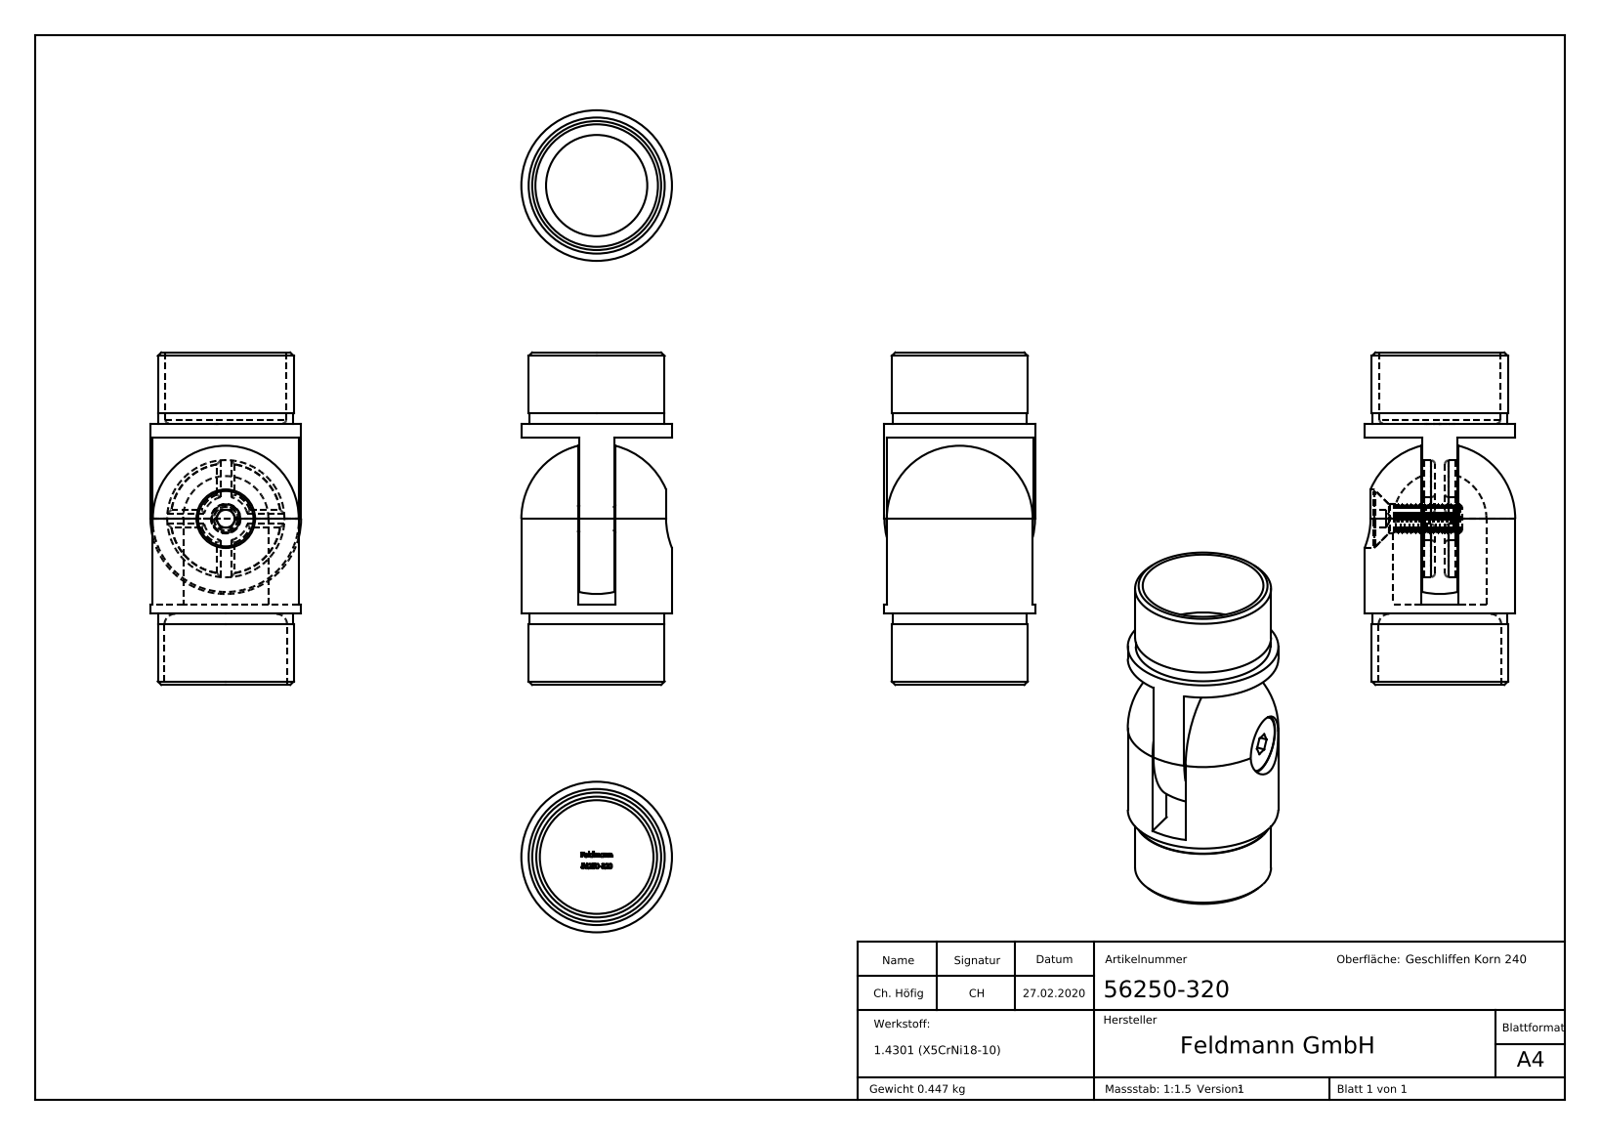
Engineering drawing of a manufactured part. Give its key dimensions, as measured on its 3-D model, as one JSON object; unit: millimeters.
{"part_name": "socket countersunk head screw_din_DIN 7991 - M8 x 25 --- 25S; 5625X-320 Teil2; 5625X-320 Teil1_56250-320 Teil1; 5625X-320 Teil2_56250-320 Teil2 (+3 more)", "step_written_by": "SolidWorks 2015 (CONFIG_CONTROL_DESIGN)", "units": "millimeters", "bodies": {"solids": 3, "faces": 403, "planar": 168, "cylindrical": 56, "other": 179}, "overall_size": [93.6, 42.4, 42.4], "volume_mm3": 57804, "surface_area_mm2": 29843, "round_holes": [[6.8, 1], [8.2, 1], [16.5, 1], [33, 1], [34, 1], [34.5, 1]], "round_bosses_or_shafts": [[42.4, 1], [38.3, 1], [37.9, 1], [15.57, 1], [8, 1]], "partial_cylinders_radius": [[1, 8], [6.25, 1], [13.1, 1]], "face_to_face_distances": [0.35, 10.15, 4, 49.6, 53.6, 10.5, 3.5, 3.85, 6.65, 6.3]}
